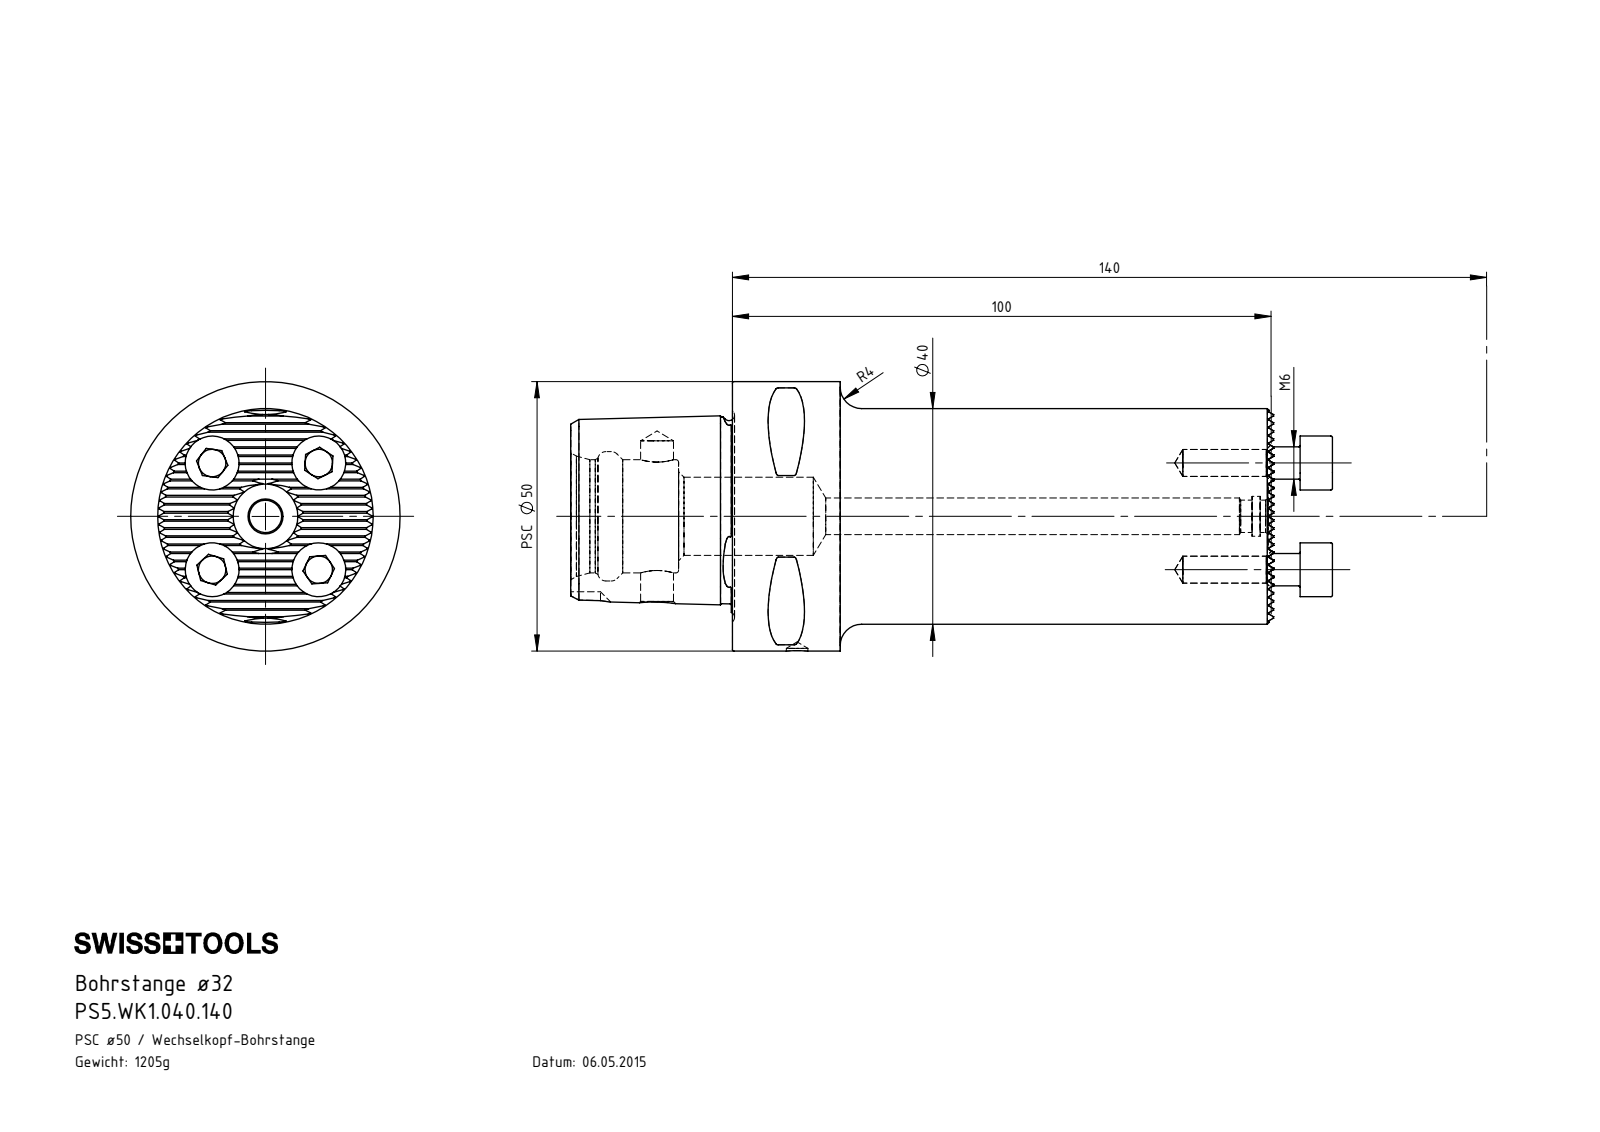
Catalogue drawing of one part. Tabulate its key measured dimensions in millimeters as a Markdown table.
| quantity | value |
| --- | --- |
| part name | PS5-WK1.040.140; DIN 3771 - 6x1; ISO 4762 - M6 x 16; PS5-WK1.040.140_A |
| STEP written by | SolidWorks 2012 (AUTOMOTIVE_DESIGN) |
| units | millimeters |
| bodies | 6 solids, 486 faces (242 planar, 111 cylindrical, 133 other) |
| overall size | 141.4 × 50 × 50 |
| volume | 153 427 mm³ |
| surface area | 29 008 mm² |
| round holes (diameter × count) | 5 × 4, 4 × 1, 6 × 1, 6.1 × 1, 6.8 × 1, 7.4 × 1, 14.5 × 1, 21 × 1, 24 × 1 |
| round bosses / shafts (diameter × count) | 10 × 4, 6 × 4, 50 × 1, 40 × 1 |
| partial cylindrical surfaces (radius × count) | 0.12 × 27, 0.5 × 8, 4 × 1 |
| main face-to-face distances | 1.3, 2.6, 3.9, 5.2, 12.99, 30, 9.09, 11.69, 7.79, 10.39 |
| hole center spacings | 14, 19.8, 28, 26 |
